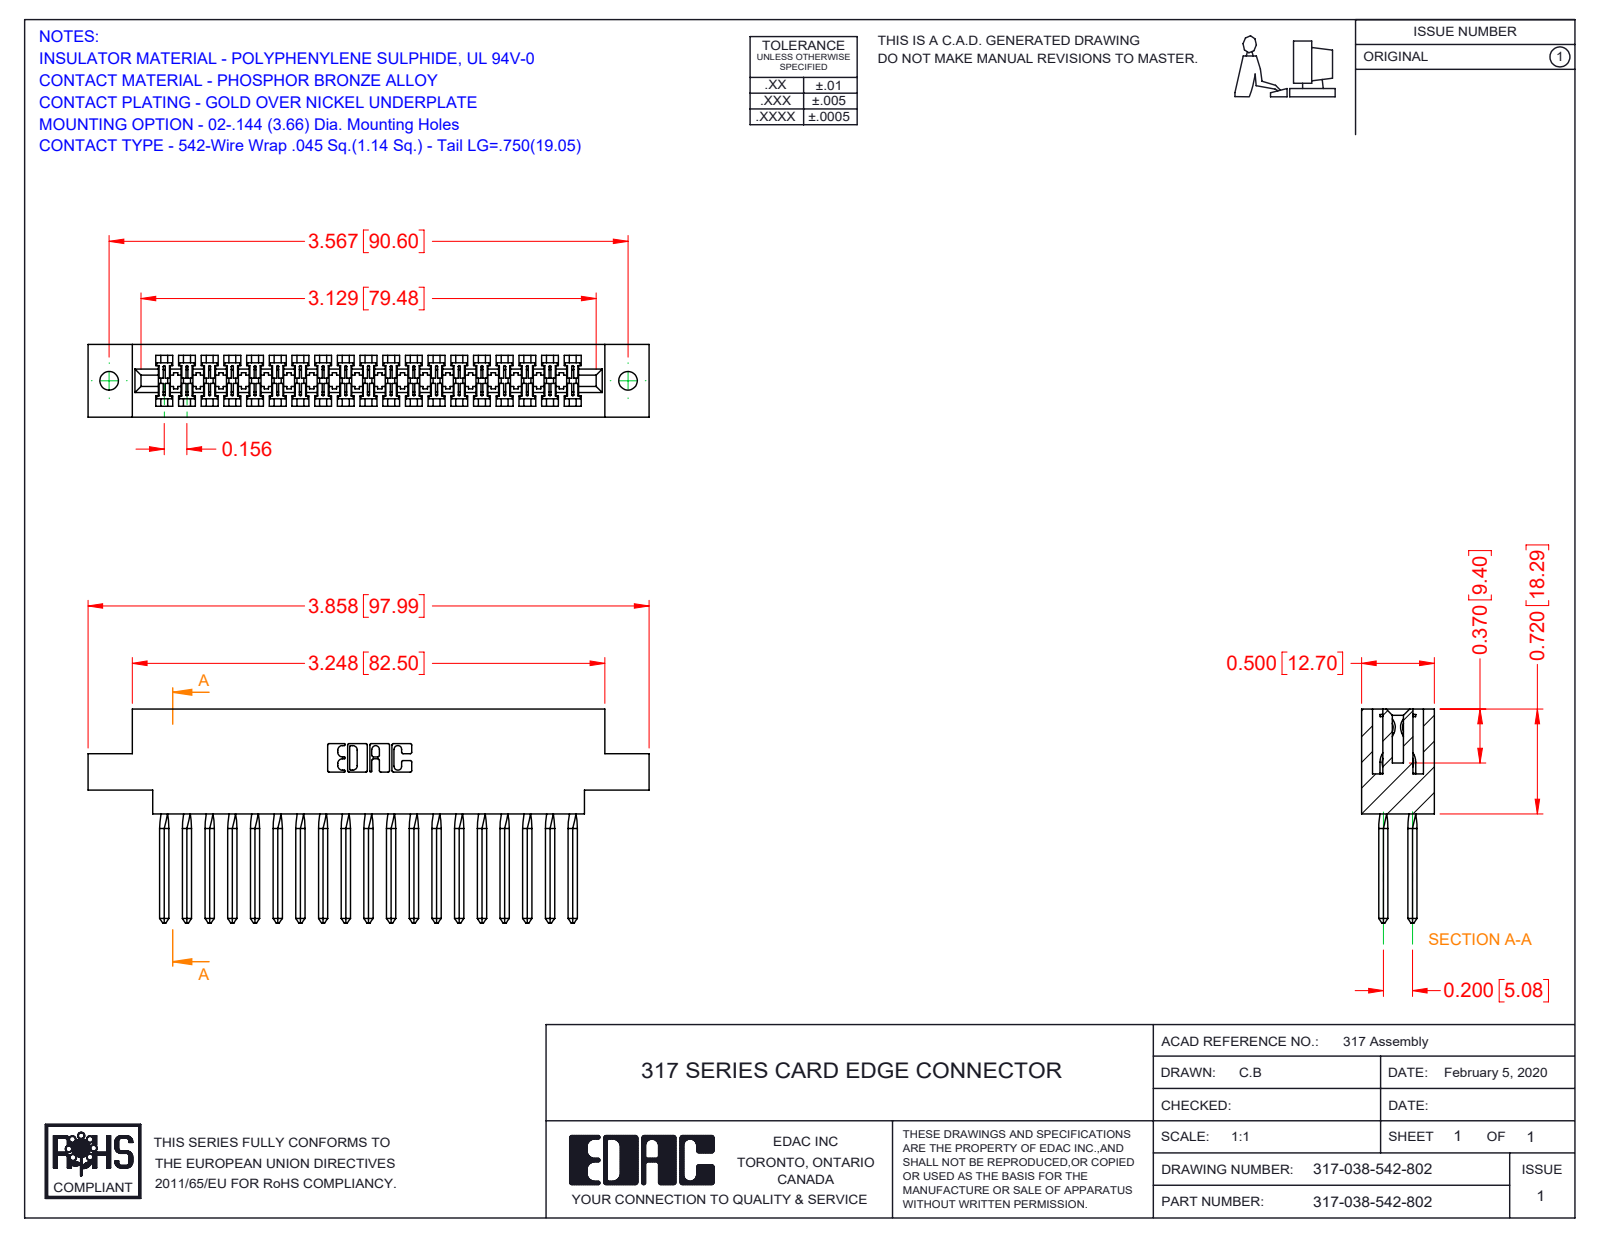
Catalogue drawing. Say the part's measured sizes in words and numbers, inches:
The part is named "317-290-003_542; 317 Part_.144 Dia; 317-038-542-802". Its 3-D file was written by "SolidWorks 2016 (CONFIG_CONTROL_DESIGN)". It is 39 solids with 2268 faces: 1806 planar, 310 cylindrical and 152 other. Overall it measures 3.858 by 1.47 by 0.5 inches. Its volume is 0.933 cubic inches and its surface area 31.38 square inches. Round holes: 2 of diameter 0.128. Partial cylindrical surfaces (rounded edges, fillets, slot ends): 76 of radius 0.006, 22 of radius 0.01, 6 of radius 0.007, 6 of radius 0.031, 3 of radius 0.026, 2 of radius 0.074, 2 of radius 0.089, 2 of radius 0.1. The main face-to-face distances are 0.5, 0.075, 0.425, 0.11, 0.35, 0.2, 0.116, 0.136, 0.72, 0.046. The hole center spacings are 3.567.
